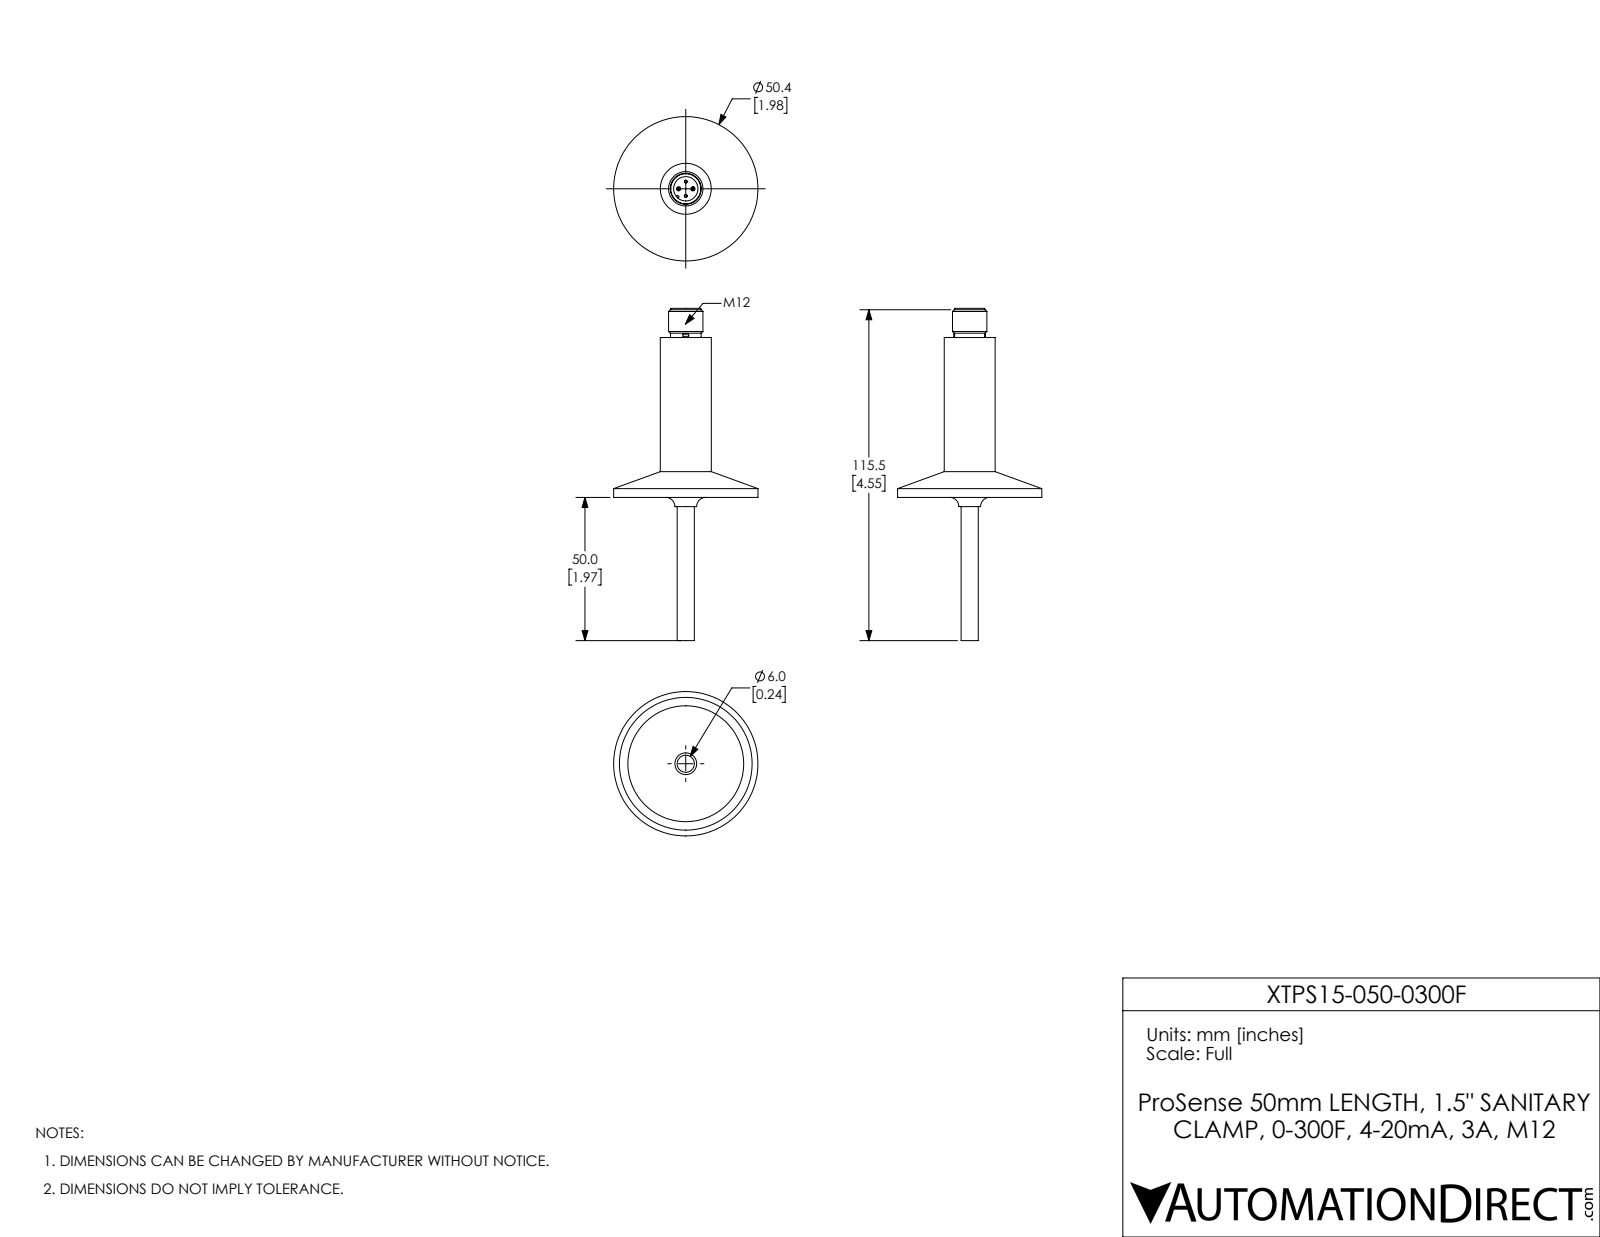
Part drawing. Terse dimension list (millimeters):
name: XTPS15-050-0300F
written by: SolidWorks 2017 (AUTOMOTIVE_DESIGN)
unit: mm
bodies: 1 solid, 79 faces (26 planar, 23 cylindrical, 30 other)
size: 116 × 50.4 × 50.4
volume: 25 270 mm³; area: 9 058 mm²
holes: 1× ⌀8.5
bosses: 4× ⌀1, 1× ⌀50.4, 1× ⌀17.8, 1× ⌀12, 1× ⌀10.7, 1× ⌀10.5, 1× ⌀6
rounds: 1× R0.4
face distances: 55.8, 57, 1.2, 66, 10.2, 9, 50, 105.8, 107, 116
